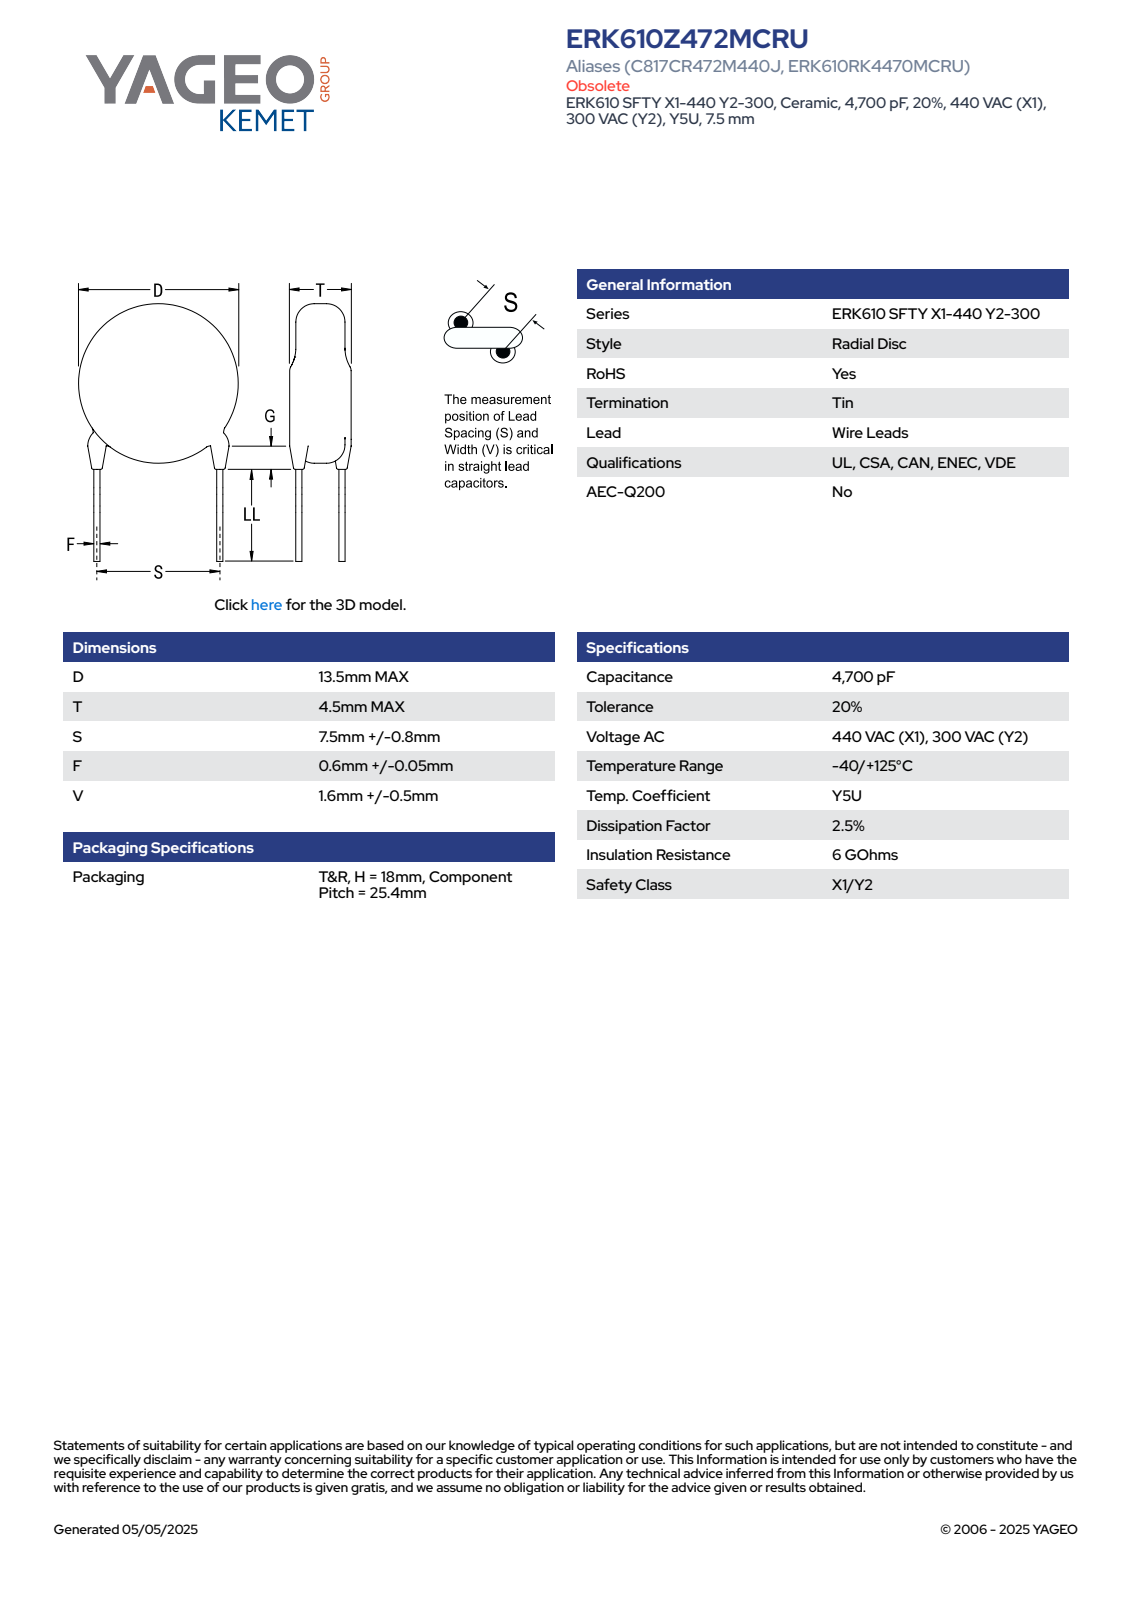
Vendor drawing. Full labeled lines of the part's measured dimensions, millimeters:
Part name (STEP PRODUCT): CCD_KST_13.5X4.5_D13.5T4.5S7.5LL11F0.65G3V2.1
STEP written by: SolidWorks 2014 (AUTOMOTIVE_DESIGN)
Units: millimetres
Bodies: 4 solids, 81 faces (63 planar, 6 cylindrical, 12 other)
Overall size (bounding box): 24.61 × 13.5 × 4.5
Volume: 635 mm³ · Surface area: 507 mm²
Round bosses / shafts (diameter × count): ⌀0.65 ×2, ⌀13.5 ×1
Main face-to-face distances: 4.5, 18.7, 17.02, 1.68, 0.46, 6.86, 0.32, 1.36, 0.31, 4.98
